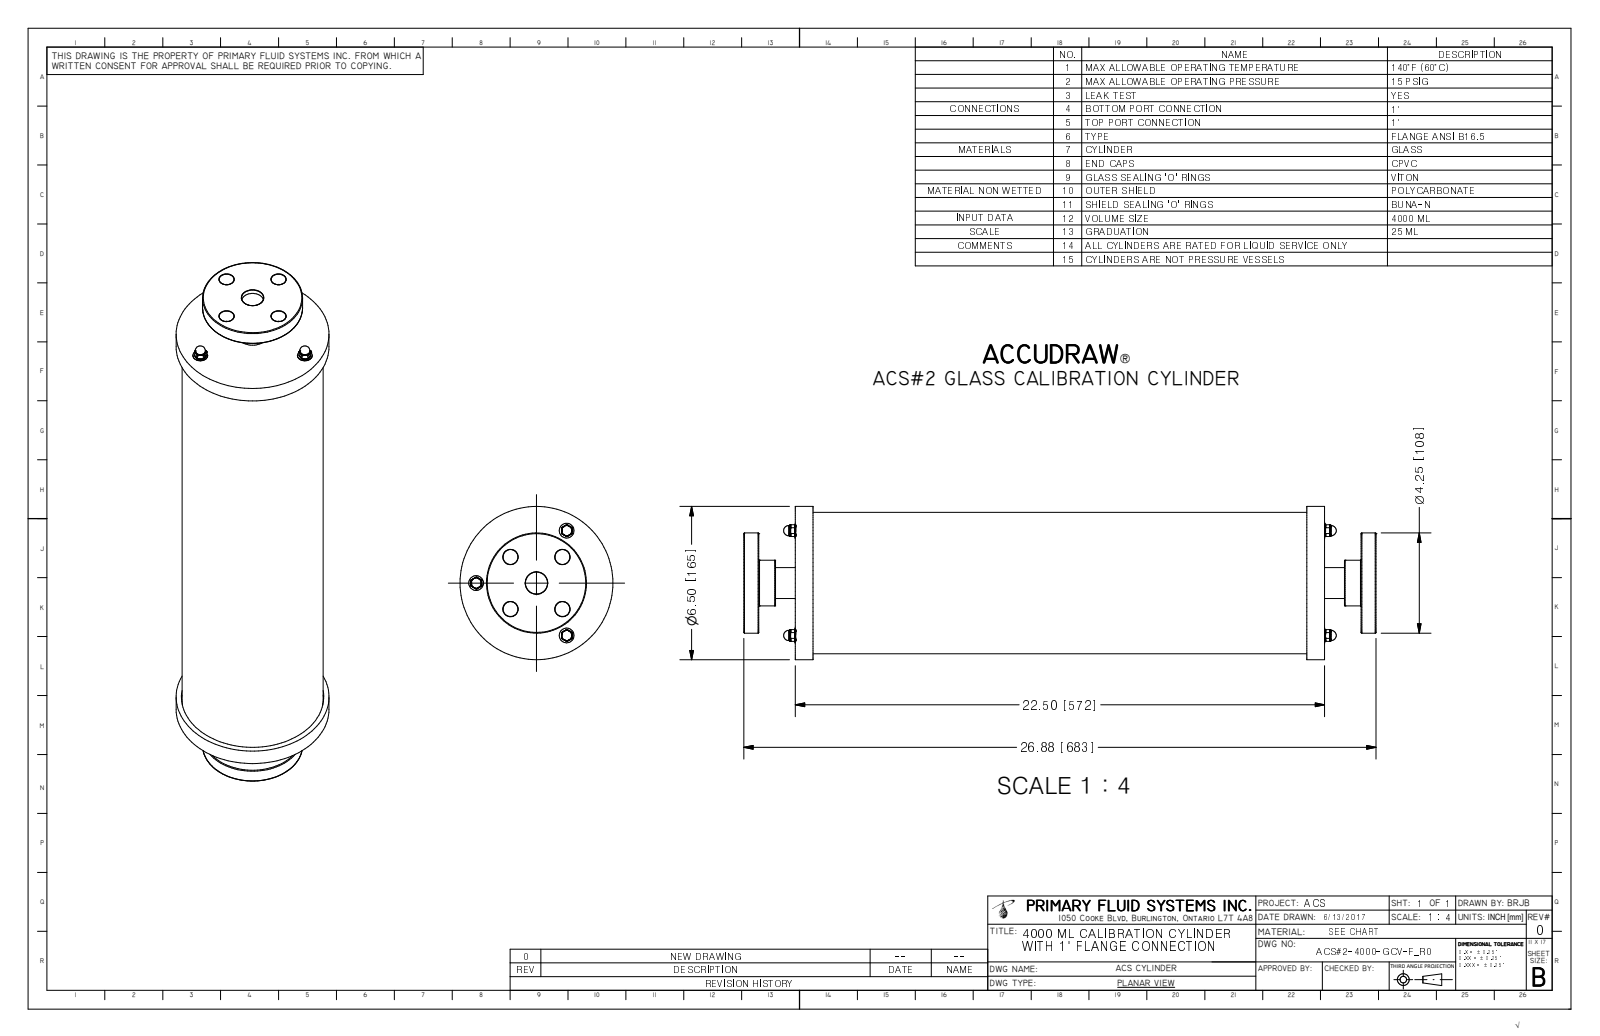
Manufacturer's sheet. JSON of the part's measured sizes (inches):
{"part_name": "ACS#2-4000-GCV-F_R0", "step_written_by": "Autodesk Inventor 2009 (AUTOMOTIVE_DESIGN)", "units": "inches", "bodies": {"solids": 1, "faces": 630, "planar": 33, "cylindrical": 175, "other": 422}, "overall_size": [26.88, 6.5, 6.5], "volume_in3": 175.5, "surface_area_in2": 1715, "round_holes": [[0.63, 4], [0.266, 3], [0.281, 3], [0.936, 1], [0.957, 1], [4.134, 1], [4.625, 1], [5.75, 1], [6.05, 1]], "round_bosses_or_shafts": [[0.625, 3], [0.25, 3], [6.5, 1], [6, 1], [5.7, 1], [4.528, 1], [4.25, 1], [4, 1]], "face_to_face_distances": [0.75, 21.75, 22.5, 2.19, 2.94, 23.94, 24.69, 0.635, 26.245, 1.555], "hole_center_spacings": [1.562, 2.209, 2.567, 1.133, 1.833, 2.637, 3.125, 3.333]}
